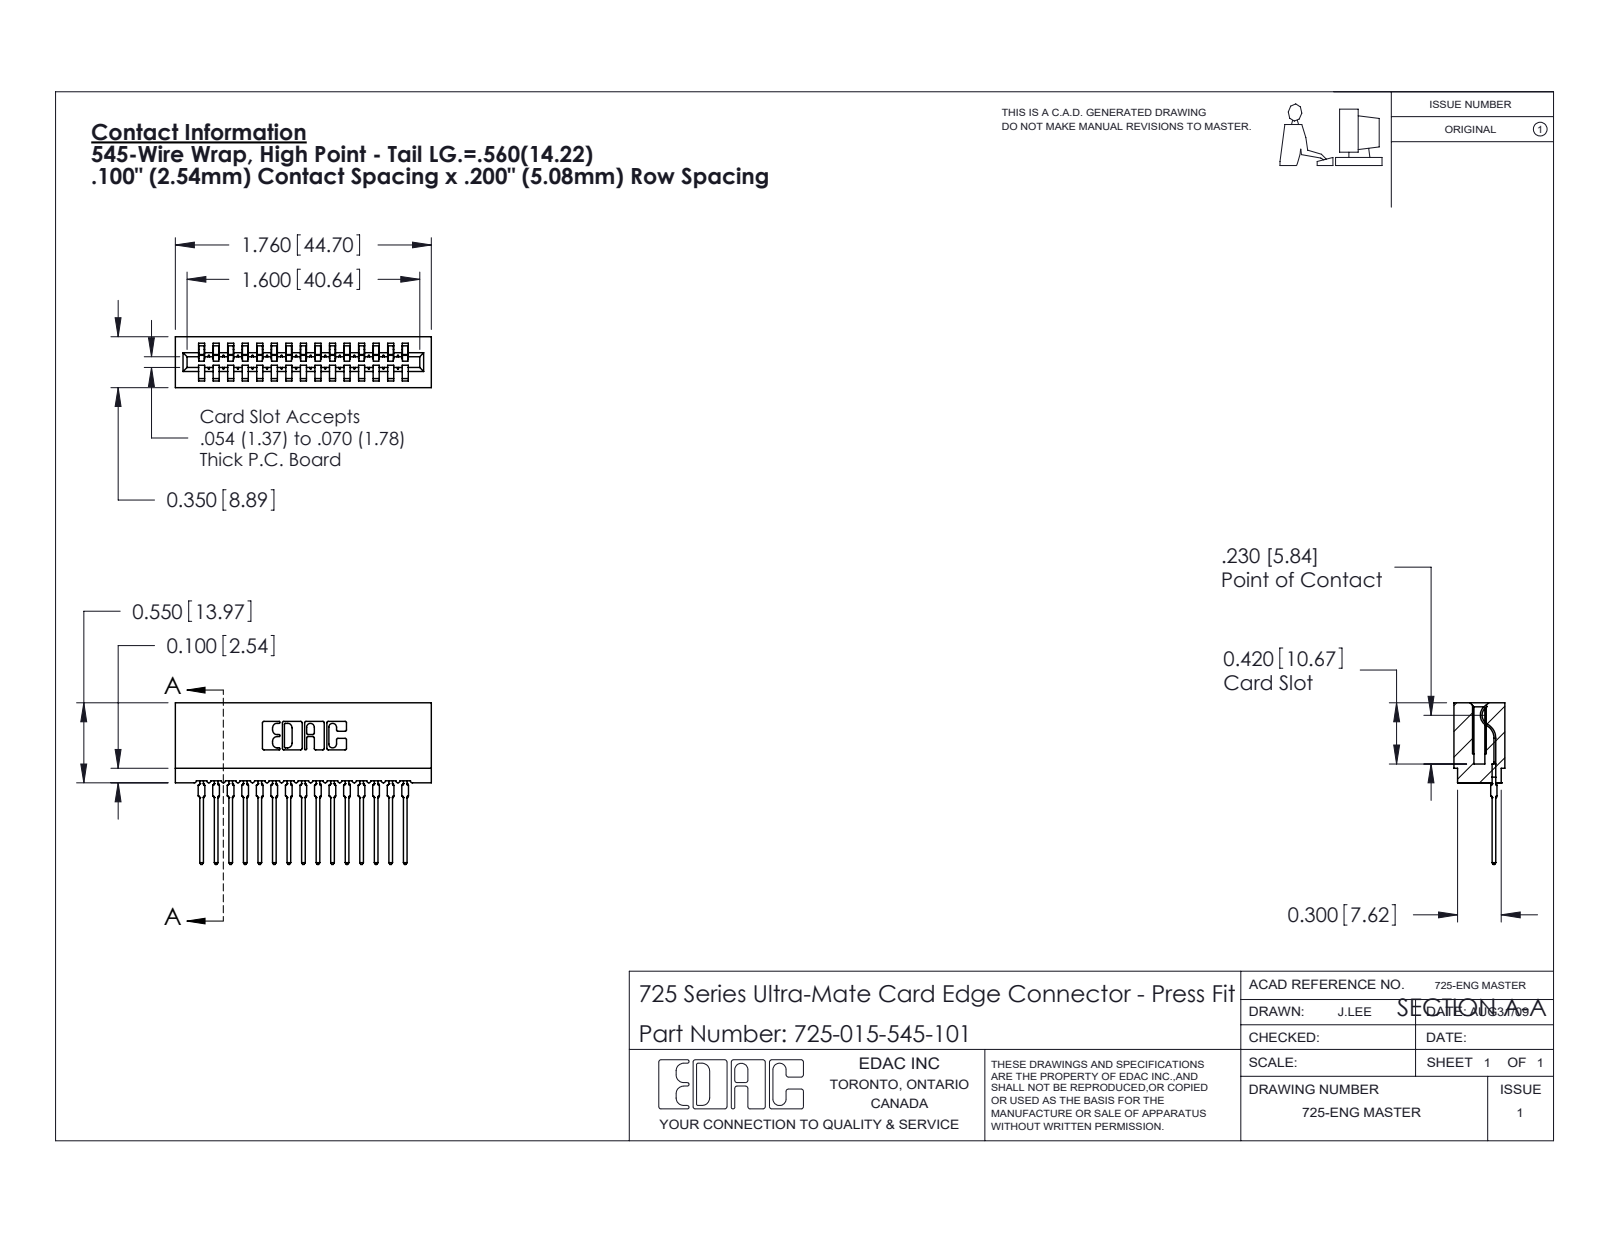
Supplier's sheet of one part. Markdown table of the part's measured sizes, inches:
| quantity | value |
| --- | --- |
| part name | 745-292-001_545; 725 Part_Insulator Option - 01; 725-015-545-101 |
| STEP written by | SolidWorks 2020 (CONFIG_CONTROL_DESIGN) |
| units | inches |
| bodies | 16 solids, 1775 faces (1060 planar, 325 cylindrical, 390 other) |
| overall size | 1.76 × 1.111 × 0.35 |
| volume | 0.219 in³ |
| surface area | 10.28 in² |
| partial cylindrical surfaces (radius × count) | 0.015 × 30, 0.021 × 30, 0.01 × 22, 0.007 × 6, 0.031 × 6, 0.005 × 4, 0.011 × 4, 0.026 × 3 |
| main face-to-face distances | 0.1, 0.2, 0.3, 0.6, 0.4, 0.5, 0.7, 0.35, 0.212, 0.138 |
